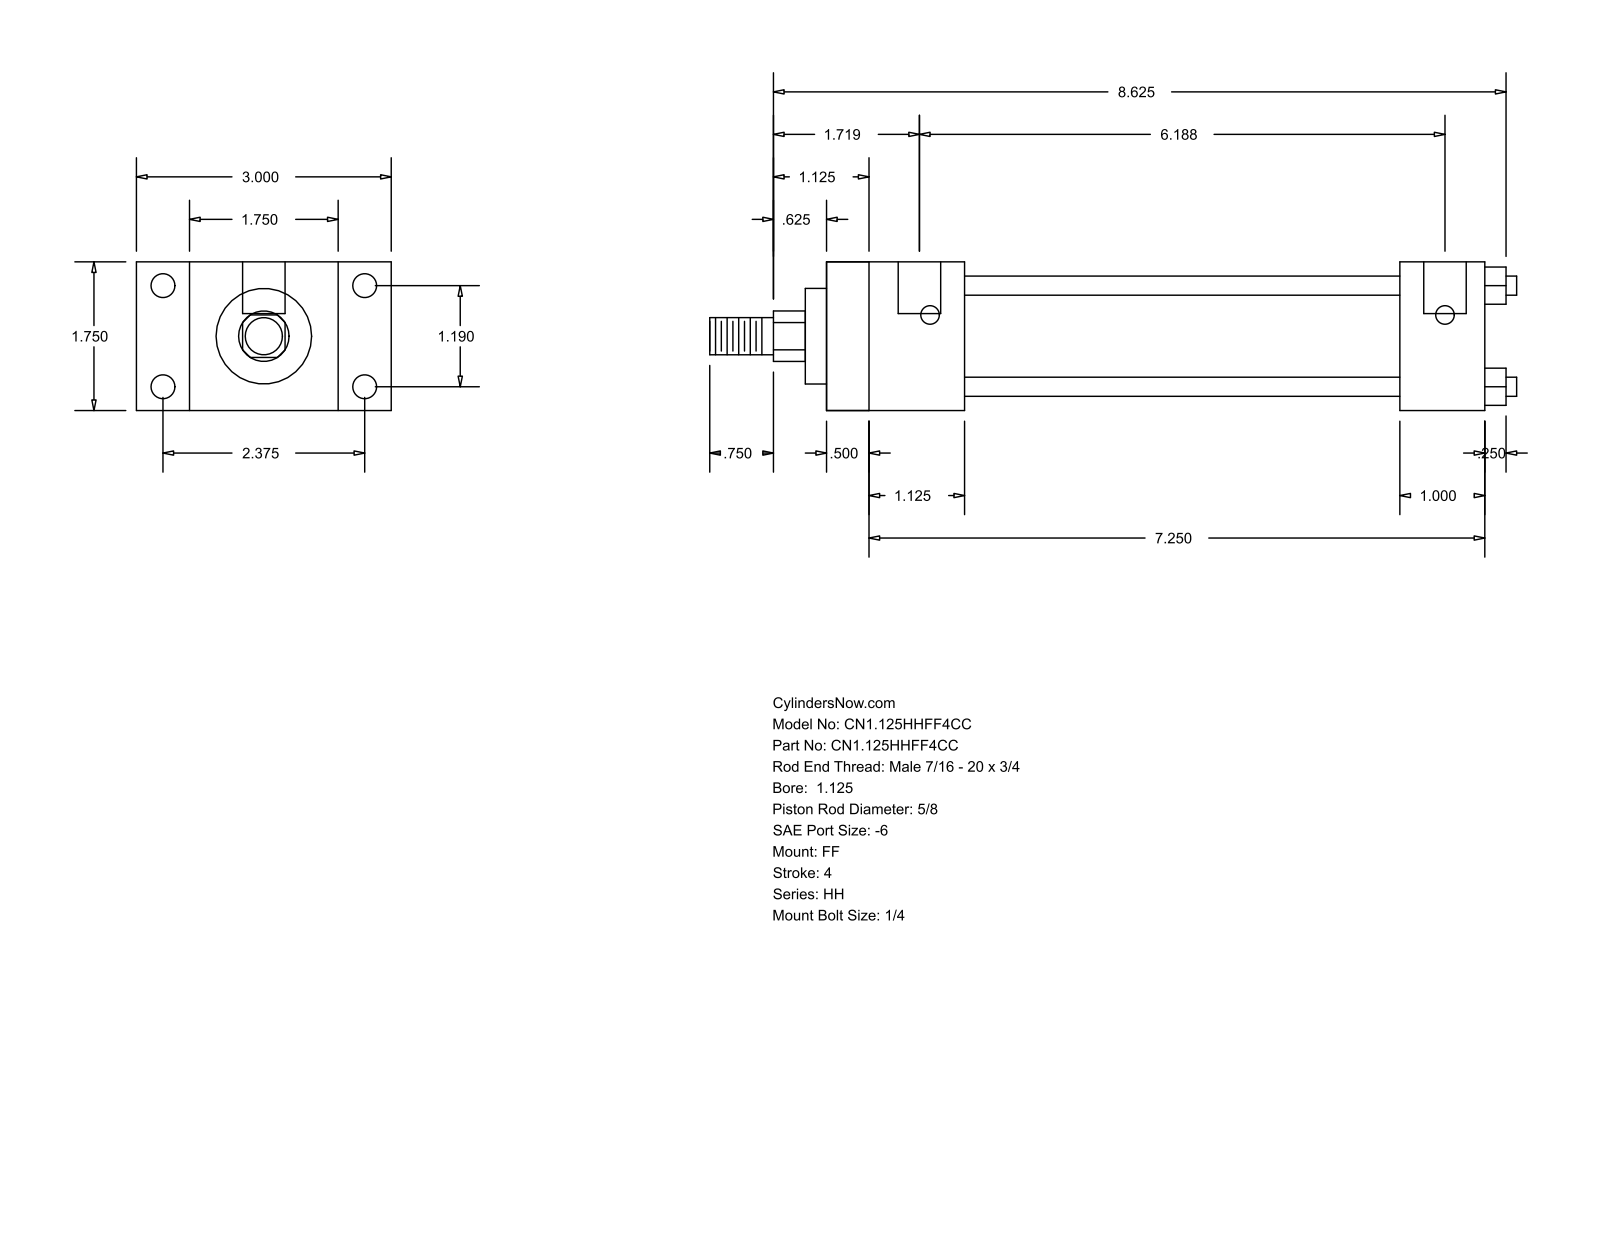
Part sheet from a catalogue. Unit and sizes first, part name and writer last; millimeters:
Units: millimetres
Overall size (bounding box): 241.3 × 76.2 × 44.45
Round holes (diameter × count): ⌀5.56 ×4, ⌀7.14 ×4, ⌀12.7 ×2
Round bosses / shafts (diameter × count): ⌀5.71 ×4, ⌀34.92 ×1, ⌀28.57 ×1, ⌀15.88 ×1, ⌀11.11 ×1
Partial cylindrical surfaces — rounded edges, fillets, slot ends (radius × count): R7.54 ×1
Main face-to-face distances: 44.46, 196.84, 12.69, 184.15, 15.87, 28.58, 60.33, 25.4, 41.27, 171.44
Hole centre spacings: 30.22, 60.32, 67.47, 153.99, 3.17, 157.16
Bodies: 0 solids, 92 faces (64 planar, 28 cylindrical, 0 other)
Part name (STEP PRODUCT): HH_FF__0112_0.625
STEP written by: GSSL Pune (CONFIG_CONTROL_DESIGN)
